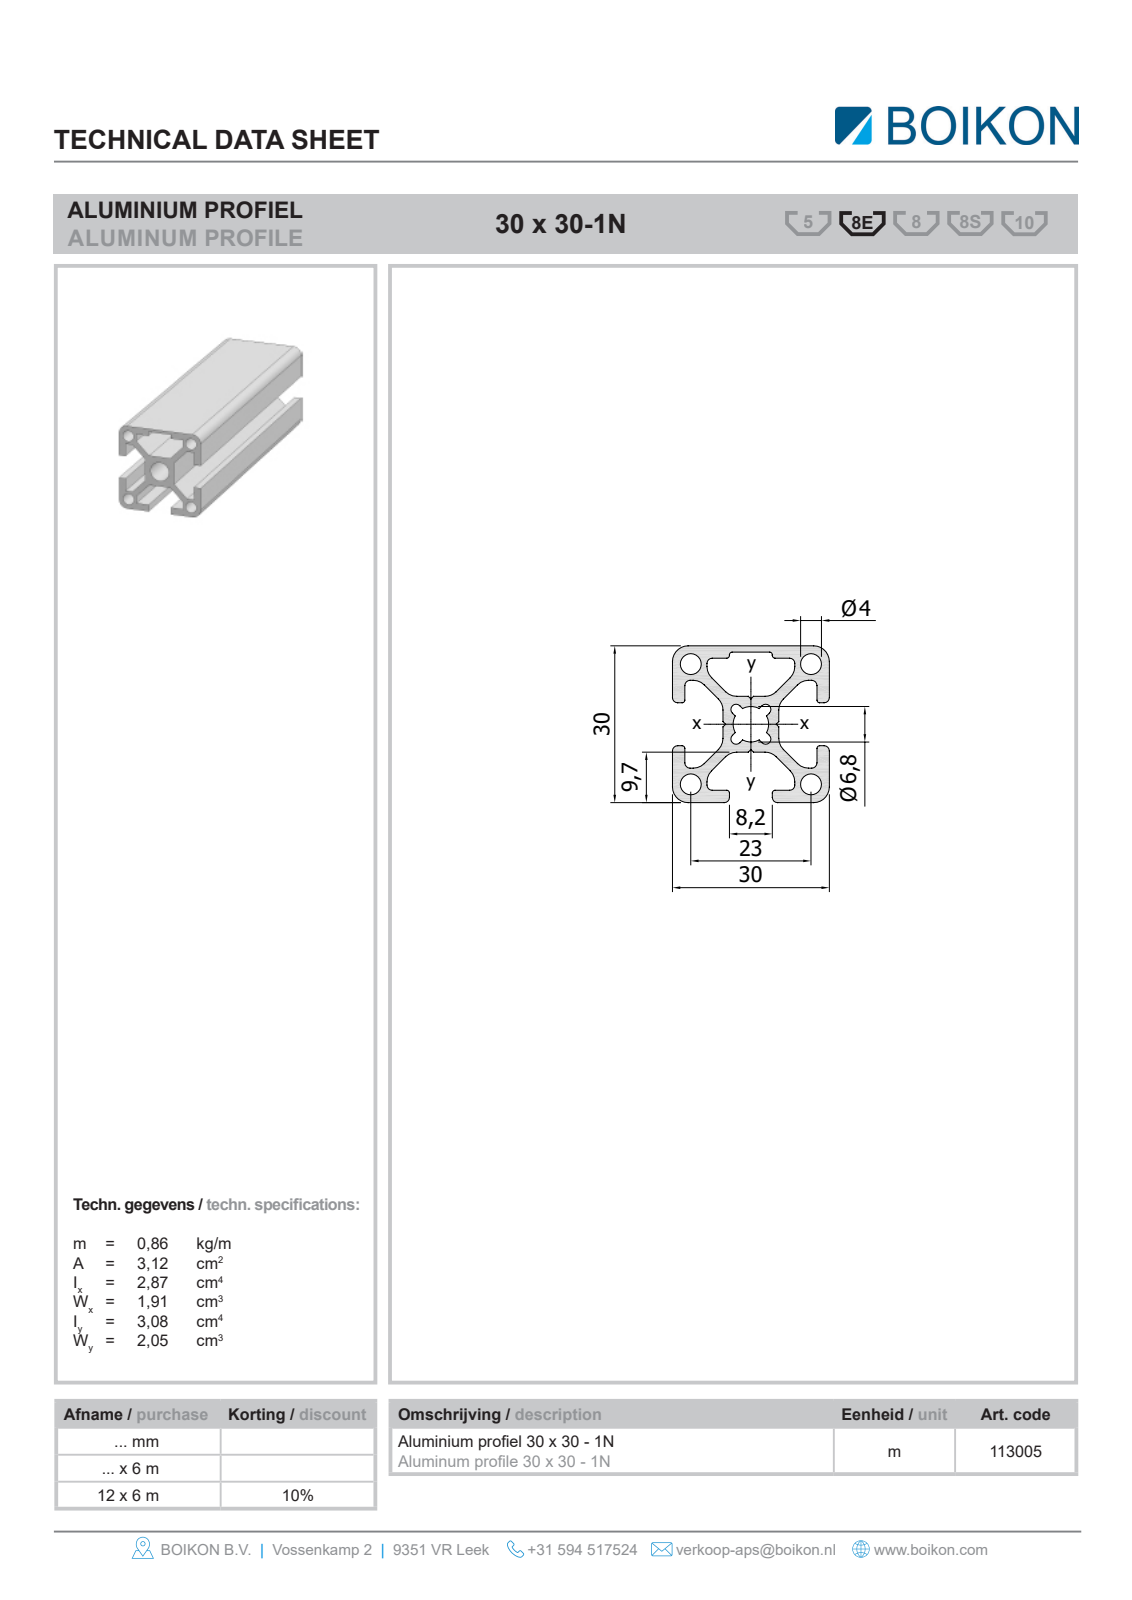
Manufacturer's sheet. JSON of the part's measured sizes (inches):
{"part_name": "Root; 11300530x30-1NBOIKON0", "step_written_by": "HiCAD 2013 1802.4 Build 509 (AUTOMOTIVE_DESIGN)", "units": "inches", "bodies": {"solids": 1, "faces": 55, "planar": 46, "cylindrical": 9, "other": 0}, "overall_size": [39.37, 1.181, 1.181], "volume_in3": 19.64, "surface_area_in2": 510, "round_holes": [[0.157, 4], [0.268, 1]], "partial_cylinders_radius": [[0.118, 4]], "face_to_face_distances": [0.094, 1.087, 1.181, 0.382, 0.799, 0.287, 0.705, 0.079, 0.252, 0.929], "hole_center_spacings": [0.64, 0.906, 1.281]}
